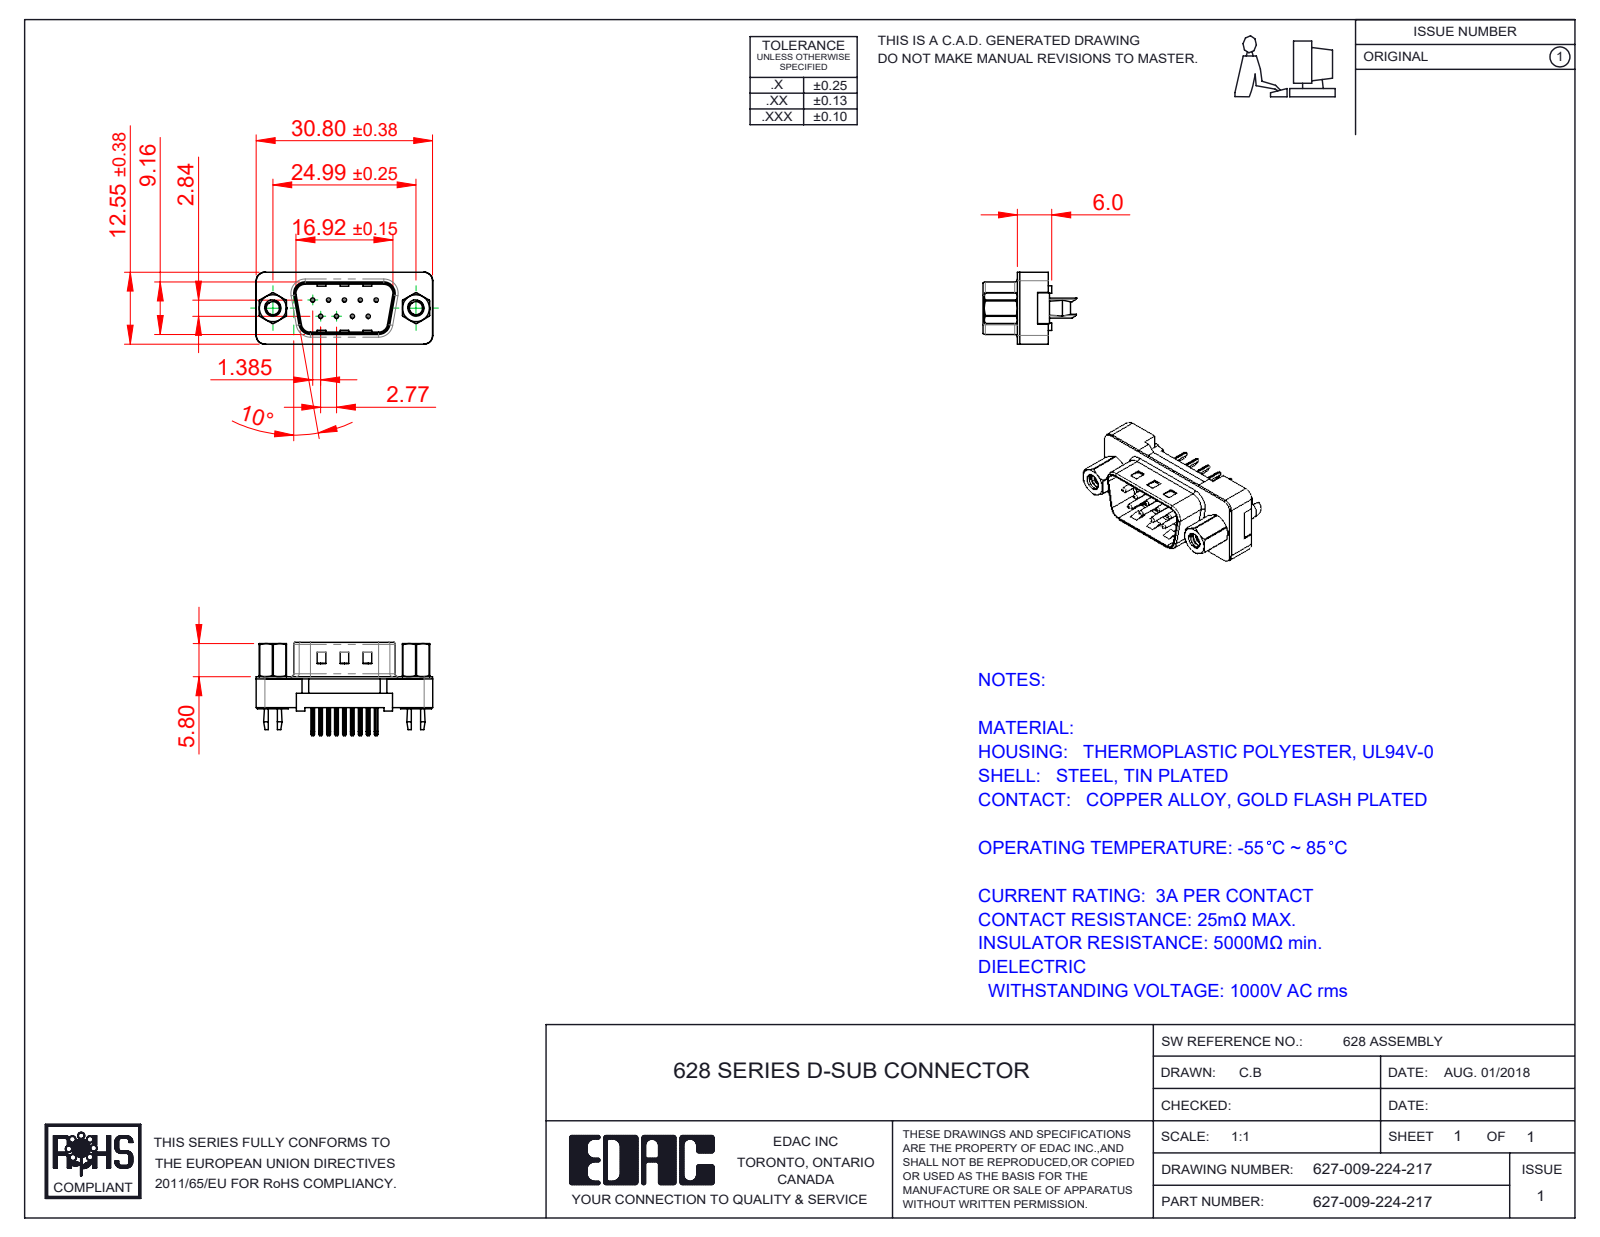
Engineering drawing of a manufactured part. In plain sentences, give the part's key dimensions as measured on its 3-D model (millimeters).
The part is named "627 4-40 Hex Standoff; 627 Plastic Body Housing_09 Contacts; 627 PB 4-40 Threaded Rivet with Boardlock; 627-009-224-217 (+3 more)". Its 3-D file was written by "SolidWorks 2020 (CONFIG_CONTROL_DESIGN)". It is 15 solids with 925 faces: 513 planar, 306 cylindrical and 106 other. Overall it measures 30.81 by 16.3 by 12.55 millimeters. Its volume is 1 894 cubic millimeters and its surface area 3 962 square millimeters. Round holes: 9 of diameter 0.35, 9 of diameter 0.85, 2 of diameter 2.26, 2 of diameter 2.29, 2 of diameter 4, 2 of diameter 4.8, 2 of diameter 5. Round bosses or shafts: 9 of diameter 0.75, 2 of diameter 4.9, 2 of diameter 2.79. Partial cylindrical surfaces (rounded edges, fillets, slot ends): 18 of radius 0.25, 9 of radius 0.12, 8 of radius 0.5, 7 of radius 1.5, 4 of radius 0.9, 4 of radius 1.6, 4 of radius 2, 2 of radius 0.4. The main face-to-face distances are 0.4, 2.5, 5.4, 5, 1.58, 2.1, 3.5, 2.9, 8.76, 1.9. The hole center spacings are 3.16, 2.77, 5.04, 5.54, 7.49, 5.03, 7.09, 8.31.
